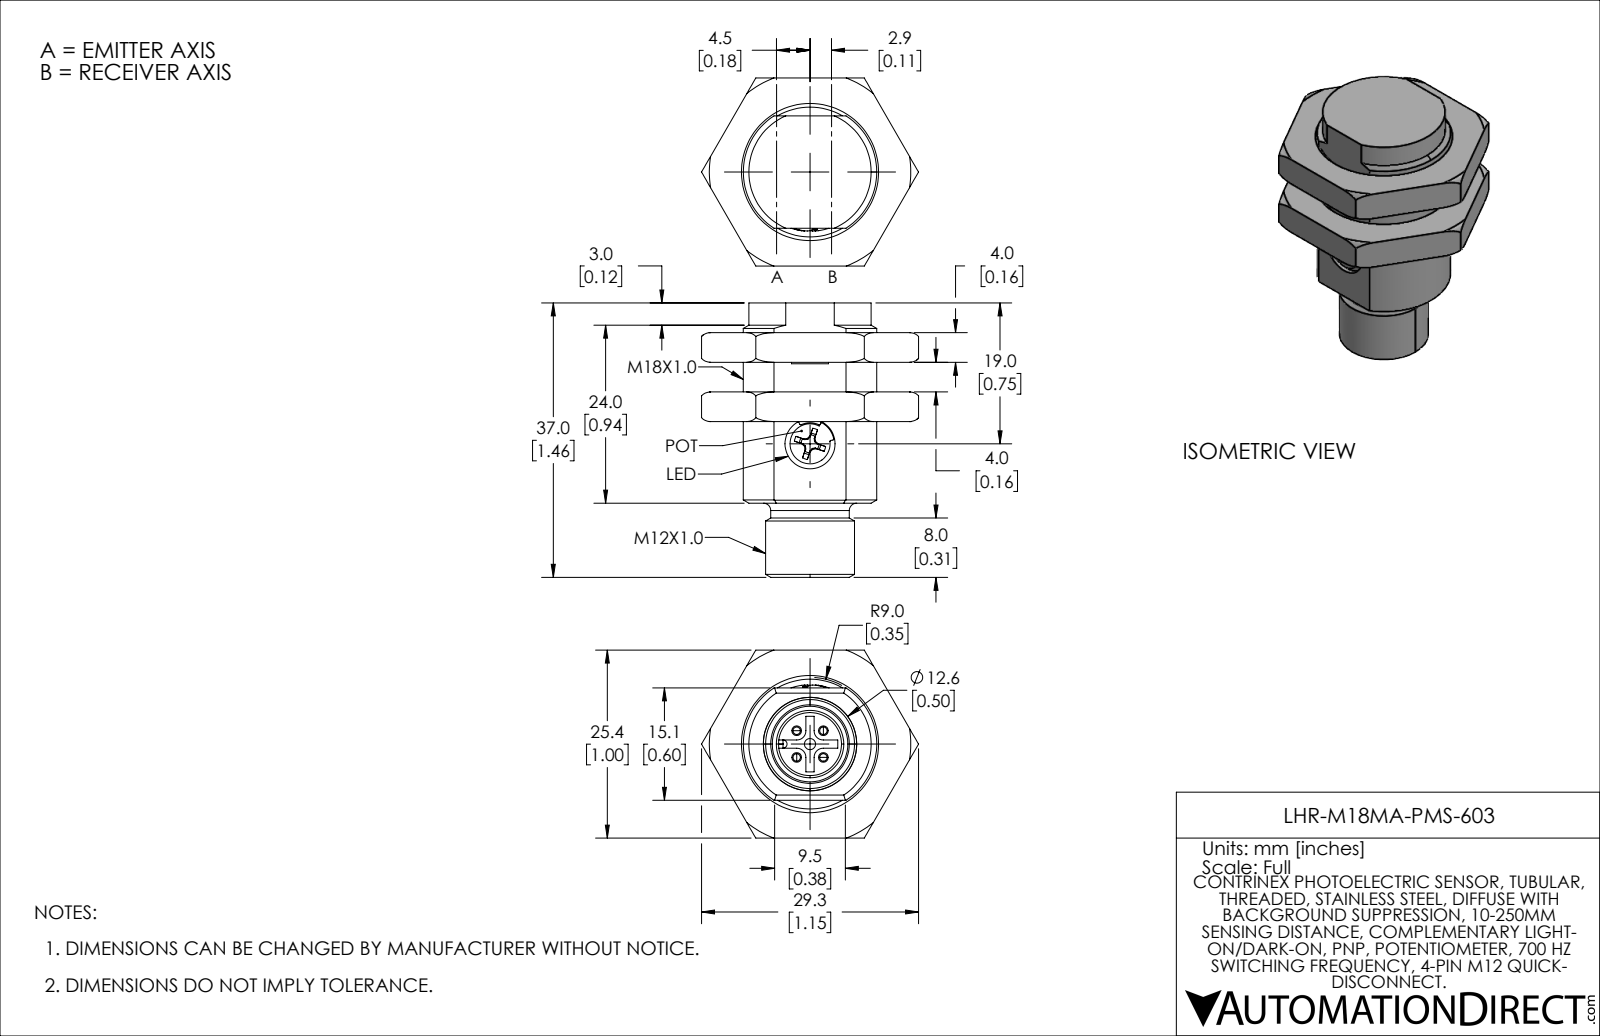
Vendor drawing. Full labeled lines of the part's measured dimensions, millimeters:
Part name (STEP PRODUCT): LHR-M18MA-PMS-603
STEP written by: SolidWorks 2021 (AUTOMOTIVE_DESIGN)
Units: millimetres
Bodies: 3 solids, 205 faces (82 planar, 56 cylindrical, 67 other)
Overall size (bounding box): 37 × 29.3 × 25.3
Volume: 9 360 mm³ · Surface area: 5 001 mm²
Round holes (diameter × count): ⌀1.5 ×1, ⌀6.8 ×1, ⌀8.5 ×1, ⌀17.5 ×1
Round bosses / shafts (diameter × count): ⌀1 ×4, ⌀12 ×1, ⌀10.6 ×1, ⌀5.4 ×1
Partial cylindrical surfaces — rounded edges, fillets, slot ends (radius × count): R0.1 ×4, R1.2 ×4, R0.1 ×3, R0.5 ×2, R0.6 ×1, R2.8 ×1, R3.3 ×1, R8.3 ×1
Main face-to-face distances: 4, 8, 12, 25.3, 5.1, 20.3, 15.2, 16, 11, 15
